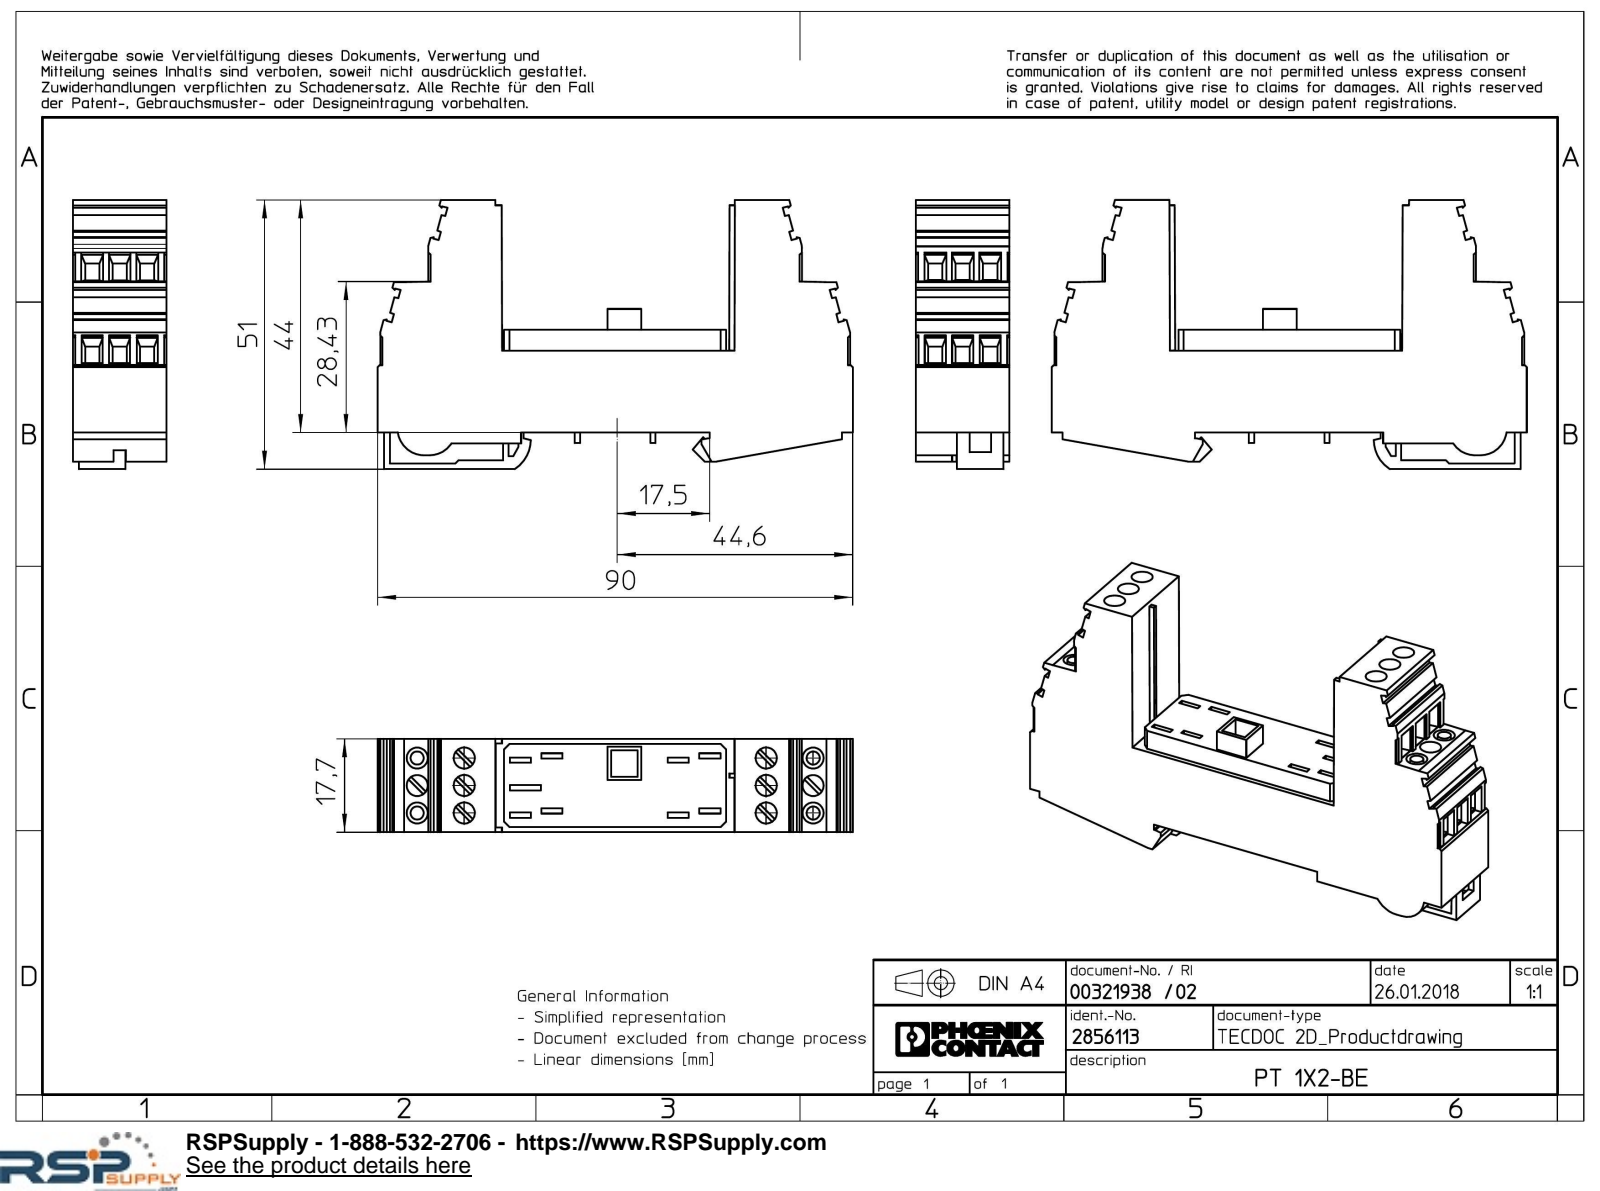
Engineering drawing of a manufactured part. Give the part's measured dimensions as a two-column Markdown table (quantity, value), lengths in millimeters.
| quantity | value |
| --- | --- |
| part name | PT_1X2_2X1...BE-select |
| STEP written by | Creo Elements/Direct Modeling 20.1A 29-Sep-2018 (C) Parametric Technology GmbH (AUTOMOTIVE_DESIGN) |
| units | millimeters |
| bodies | 1 solid, 501 faces (465 planar, 20 cylindrical, 16 other) |
| overall size | 90 × 50.95 × 17.7 |
| volume | 44 056 mm³ |
| surface area | 15 508 mm² |
| round holes (diameter × count) | 4 × 6 |
| round bosses / shafts (diameter × count) | 2.5 × 2 |
| partial cylindrical surfaces (radius × count) | 5 × 2, 3 × 1, 6.5 × 1 |
| main face-to-face distances | 17.7, 19.4, 5.2, 2.7, 1, 4.48, 15.7, 16.7, 21.5, 44 |
| hole center spacings | 5.2, 57.44, 57.2, 10.4, 58.14 |
